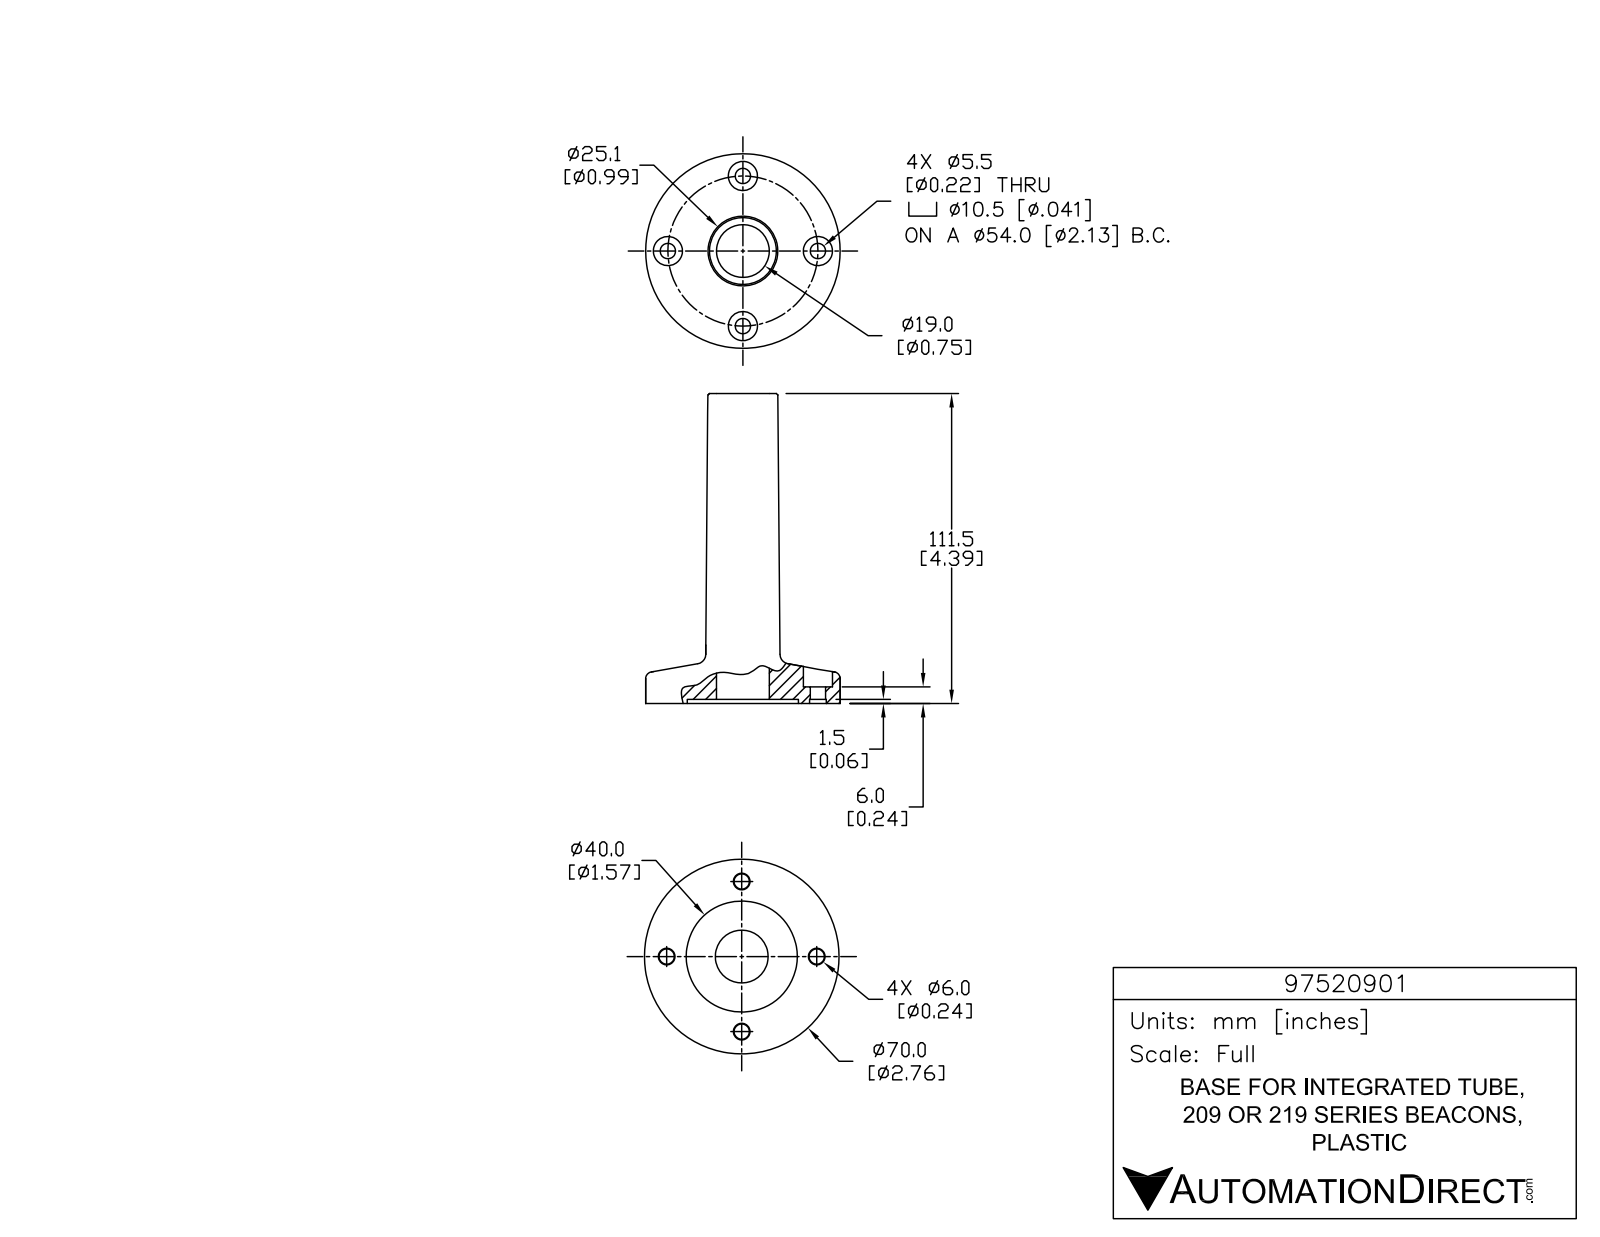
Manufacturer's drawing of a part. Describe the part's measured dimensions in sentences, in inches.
The part is named "97520901". Its 3-D file was written by "SolidWorks 2017 (AUTOMOTIVE_DESIGN)". It is 1 solid with 797 faces: 530 planar, 180 cylindrical and 87 other. Overall it measures 4.39 by 2.756 by 2.756 inches. Its volume is 3.972 cubic inches and its surface area 38.95 square inches. Round holes: 4 of diameter 0.217, 4 of diameter 0.236, 4 of diameter 0.413, 3 of diameter 0.078, 1 of diameter 0.748, 1 of diameter 1.575. Round bosses or shafts: 3 of diameter 0.452, 3 of diameter 0.113, 1 of diameter 2.756. Partial cylindrical surfaces (rounded edges, fillets, slot ends): 9 of radius 0.007, 6 of radius 0.007, 6 of radius 0.016, 6 of radius 0.016, 6 of radius 0.016, 6 of radius 0.262, 3 of radius 0.006, 3 of radius 0.006. The main face-to-face distances are 0.059, 0.177, 0.236, 4.154, 4.331, 4.39, 0.213, 0.075, 0.033, 0.061. The hole center spacings are 1.063, 1.503, 2.126.
